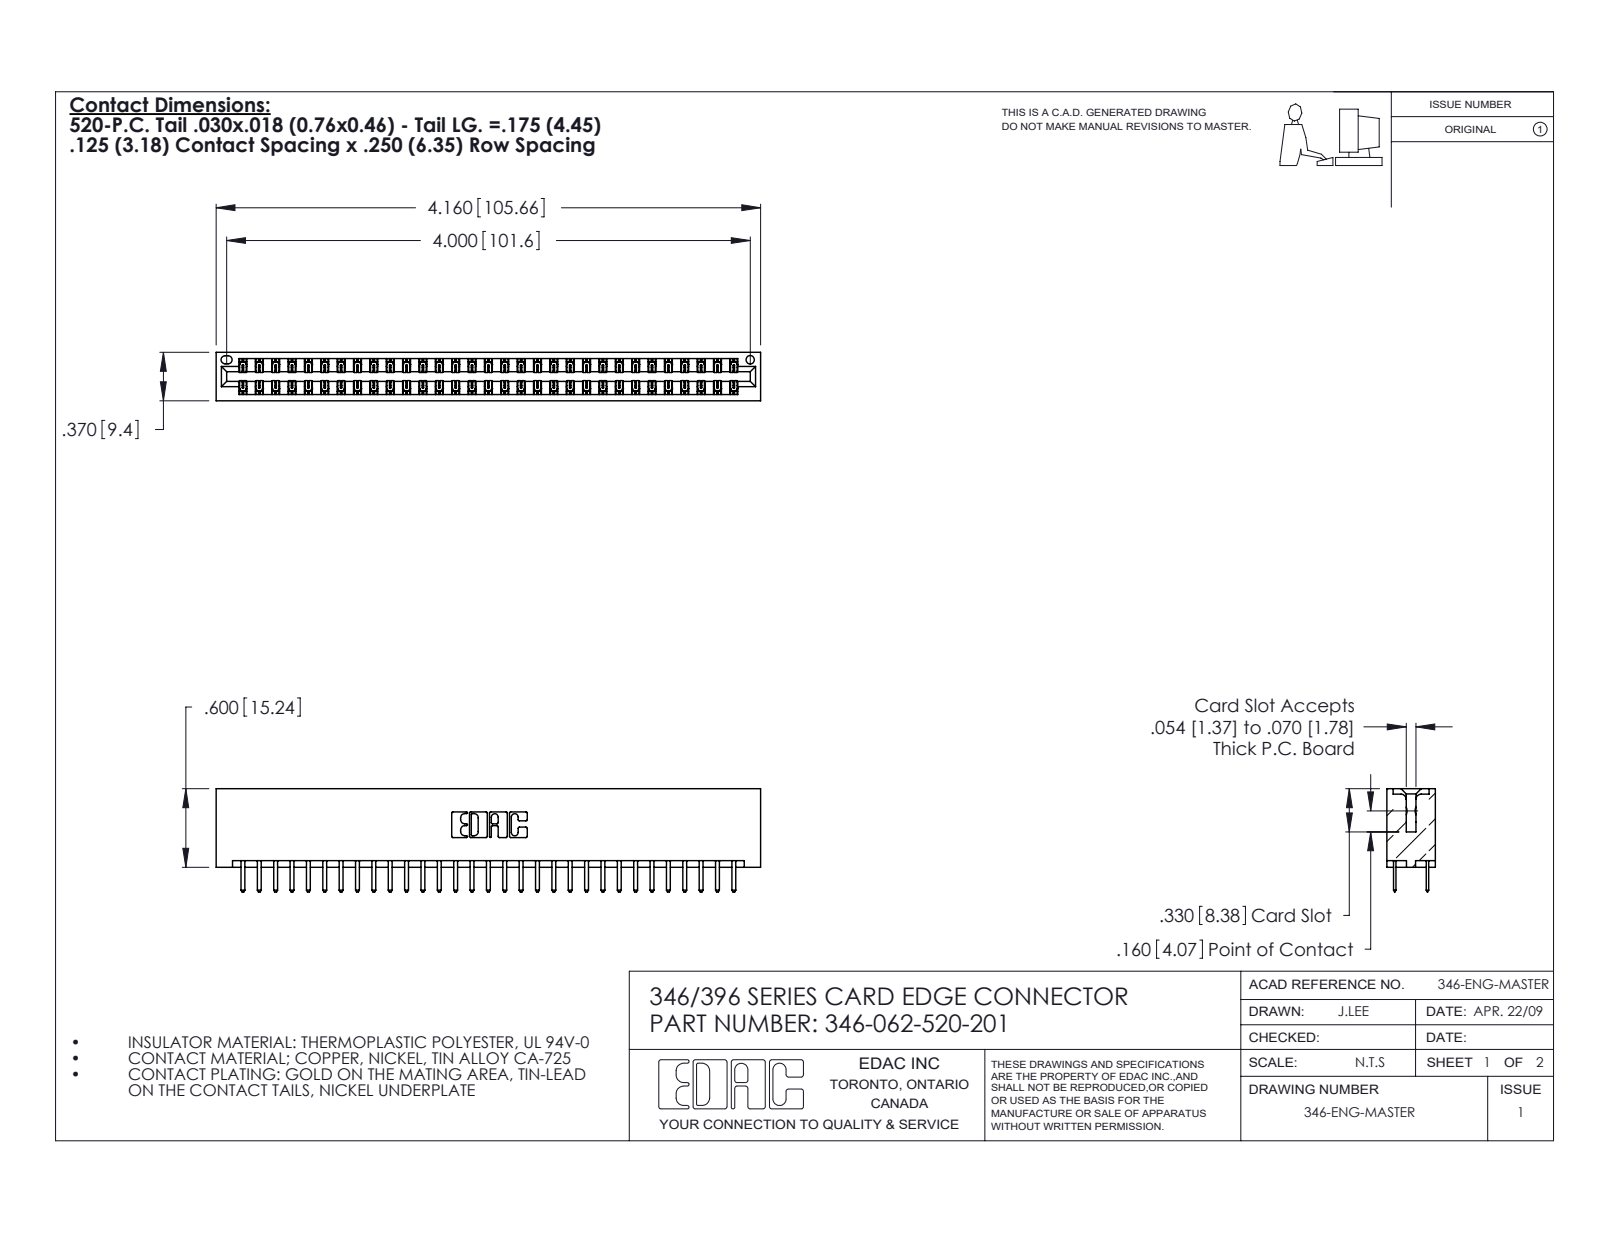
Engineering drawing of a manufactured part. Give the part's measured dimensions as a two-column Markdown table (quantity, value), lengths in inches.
| quantity | value |
| --- | --- |
| part name | 346 Part_No Mounting Lugs; 345-292-001_345-293-120; 346-062-520-201 |
| STEP written by | SolidWorks 2020 (CONFIG_CONTROL_DESIGN) |
| units | inches |
| bodies | 63 solids, 3586 faces (2366 planar, 1220 cylindrical, 0 other) |
| overall size | 4.16 × 0.788 × 0.37 |
| volume | 0.657 in³ |
| surface area | 22.82 in² |
| round holes (diameter × count) | 0.064 × 1 |
| partial cylindrical surfaces (radius × count) | 0.006 × 93, 0.01 × 66, 0.01 × 22, 0.007 × 6, 0.031 × 6, 0.026 × 3, 0.014 × 2, 0.022 × 2 |
| main face-to-face distances | 0.048, 0.322, 0.25, 0.37, 0.275, 0.072, 0.298, 0.025, 0.148, 0.222 |
